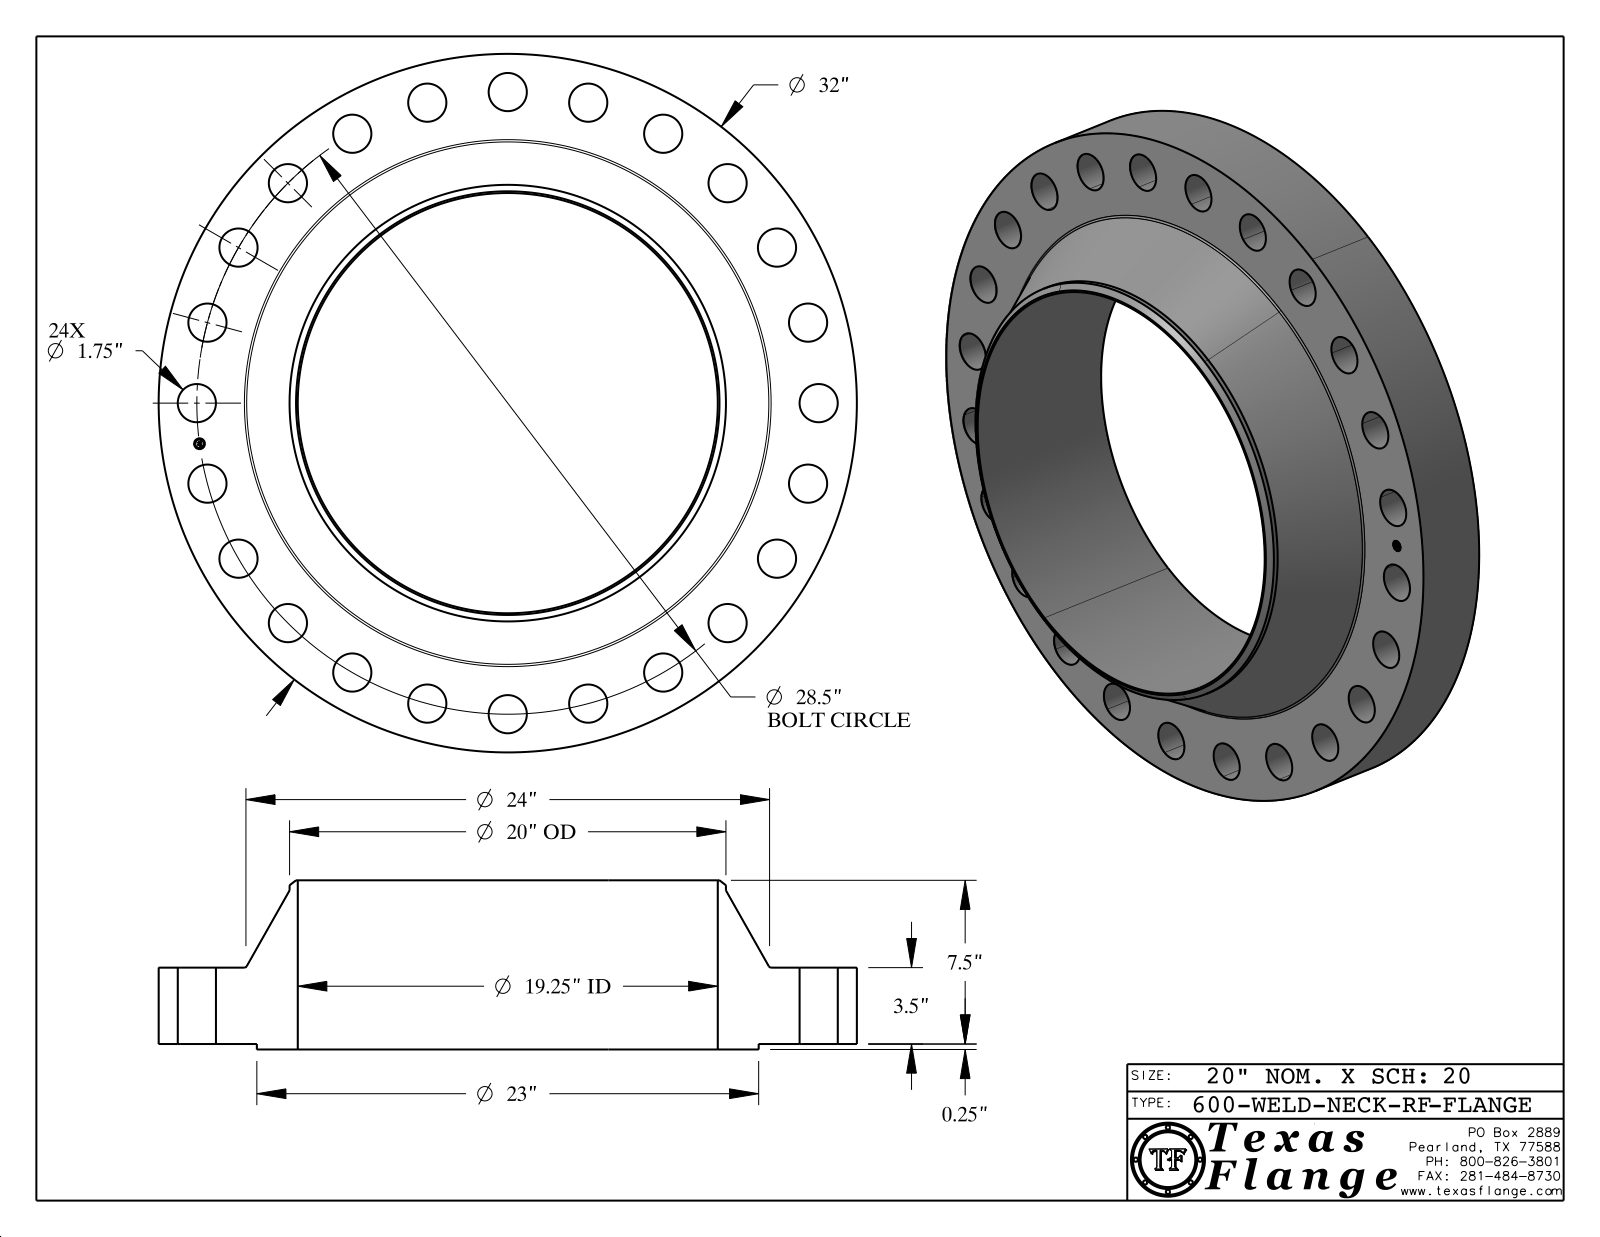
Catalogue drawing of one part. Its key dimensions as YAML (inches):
part_name: "600-WELD-NECK-RF"
step_written_by: "CATIA V5 STEP AP214 (AUTOMOTIVE_DESIGN)"
units: inches
bodies: {solids: 1, faces: 451, planar: 369, cylindrical: 76, other: 6}
overall_size: [32, 32, 7.75]
volume: 1953
surface_area: 2373
round_holes:
  - {diameter: 1.75, count: 24}
  - {diameter: 0.495, count: 1}
  - {diameter: 19.25, count: 1}
round_bosses_or_shafts:
  - {diameter: 0.03, count: 8}
  - {diameter: 32, count: 1}
  - {diameter: 23, count: 1}
  - {diameter: 20, count: 1}
  - {diameter: 0.39, count: 1}
face_to_face_distances: [3.5, 0.25, 3.75, 7.75, 7.5, 4, 0.015, 3.735, 3.485, 4.015]
hole_center_spacings: [14.25, 3.72, 7.376, 24.682, 26.331, 27.529, 20.153, 10.907]
